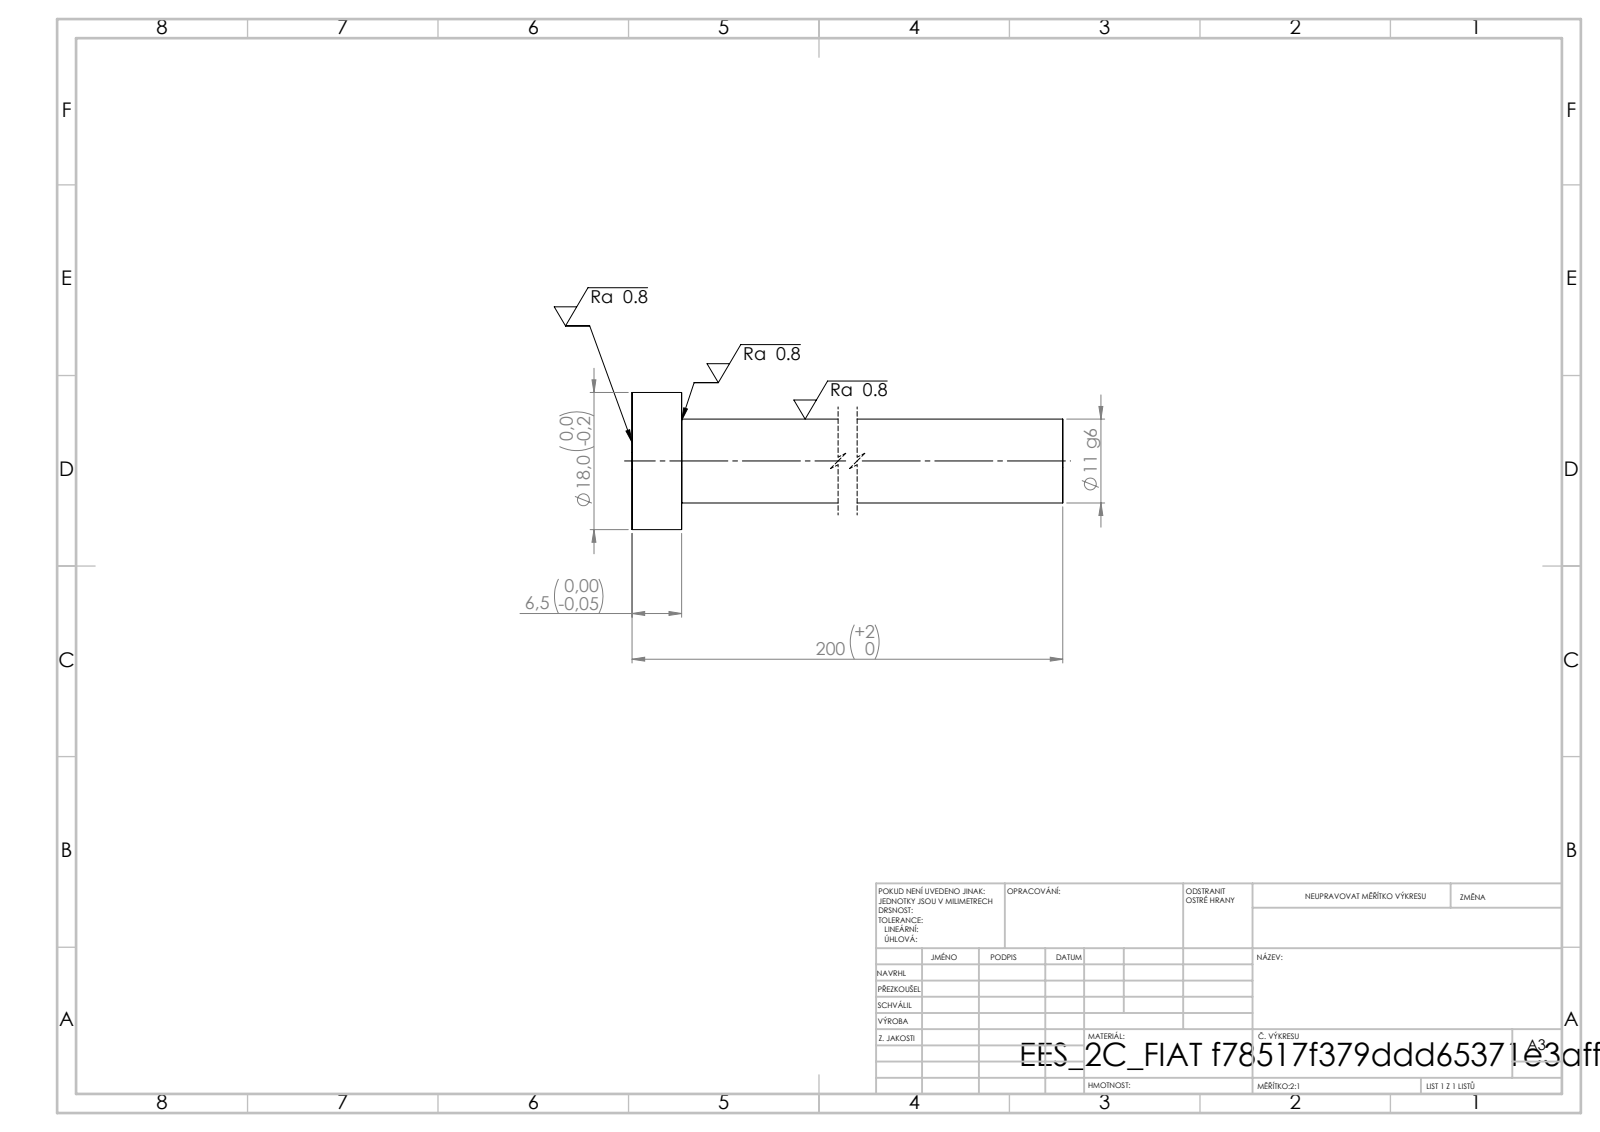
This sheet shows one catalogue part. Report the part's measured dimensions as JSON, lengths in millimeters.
{"step_written_by": "SolidWorks 2019 (CONFIG_CONTROL_DESIGN)", "units": "millimeters", "bodies": {"solids": 1, "faces": 7, "planar": 3, "cylindrical": 4, "other": 0}, "overall_size": [200, 18, 18], "volume_mm3": 20043, "surface_area_mm2": 7563, "round_bosses_or_shafts": [[18, 1], [11, 1]], "face_to_face_distances": [6.5, 200, 193.5]}
